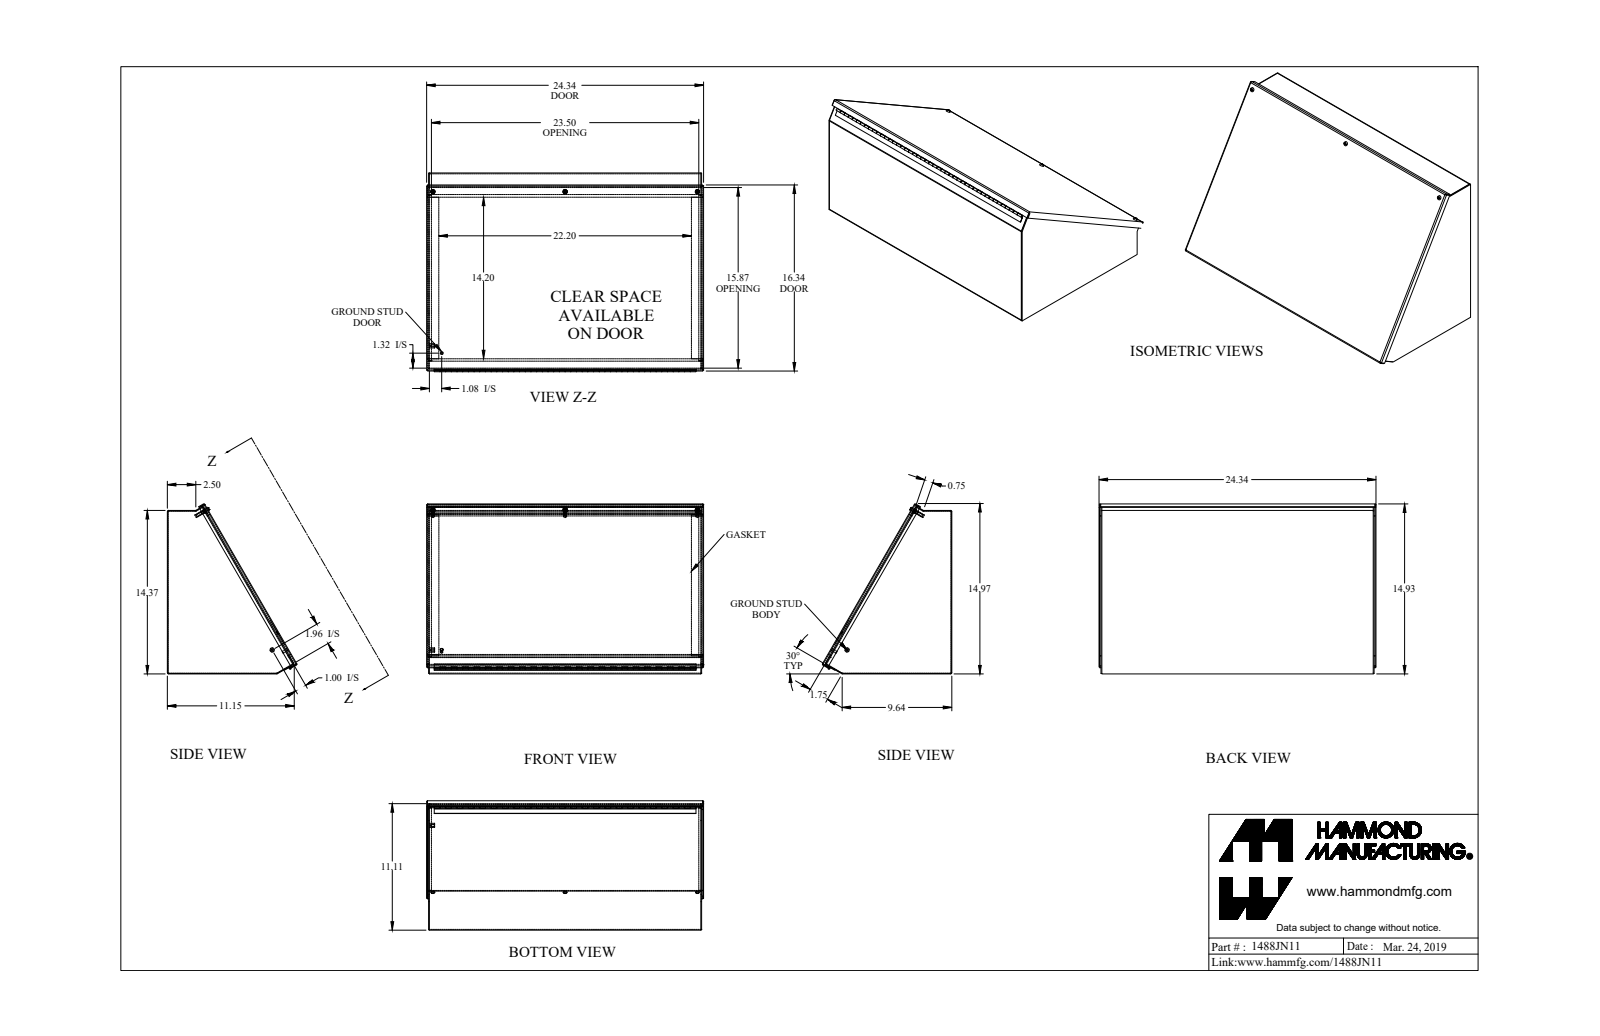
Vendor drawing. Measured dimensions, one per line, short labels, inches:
name: 1488JN11_Default
written by: SolidWorks 2019 (CONFIG_CONTROL_DESIGN)
unit: in
bodies: 20 solids, 739 faces (492 planar, 215 cylindrical, 32 other)
size: 24.343 × 14.933 × 11.374
volume: 119.3 in³; area: 3 023 in²
holes: 3× ⌀0.159, 3× ⌀0.25, 1× ⌀0.156
bosses: 3× ⌀0.39, 3× ⌀0.275, 3× ⌀0.19, 3× ⌀0.148, 1× ⌀0.375, 1× ⌀0.25, 1× ⌀0.188, 1× ⌀0.174
rounds: 12× R0.036, 12× R0.108, 3× R0.125, 3× R0.16, 3× R0.171
face distances: 0.072, 23.928, 14.293, 23.856, 24, 0.25, 0.322, 14.365, 14.221, 0.197
hole spacings: 11.625, 11.625, 23.25, 23.25
